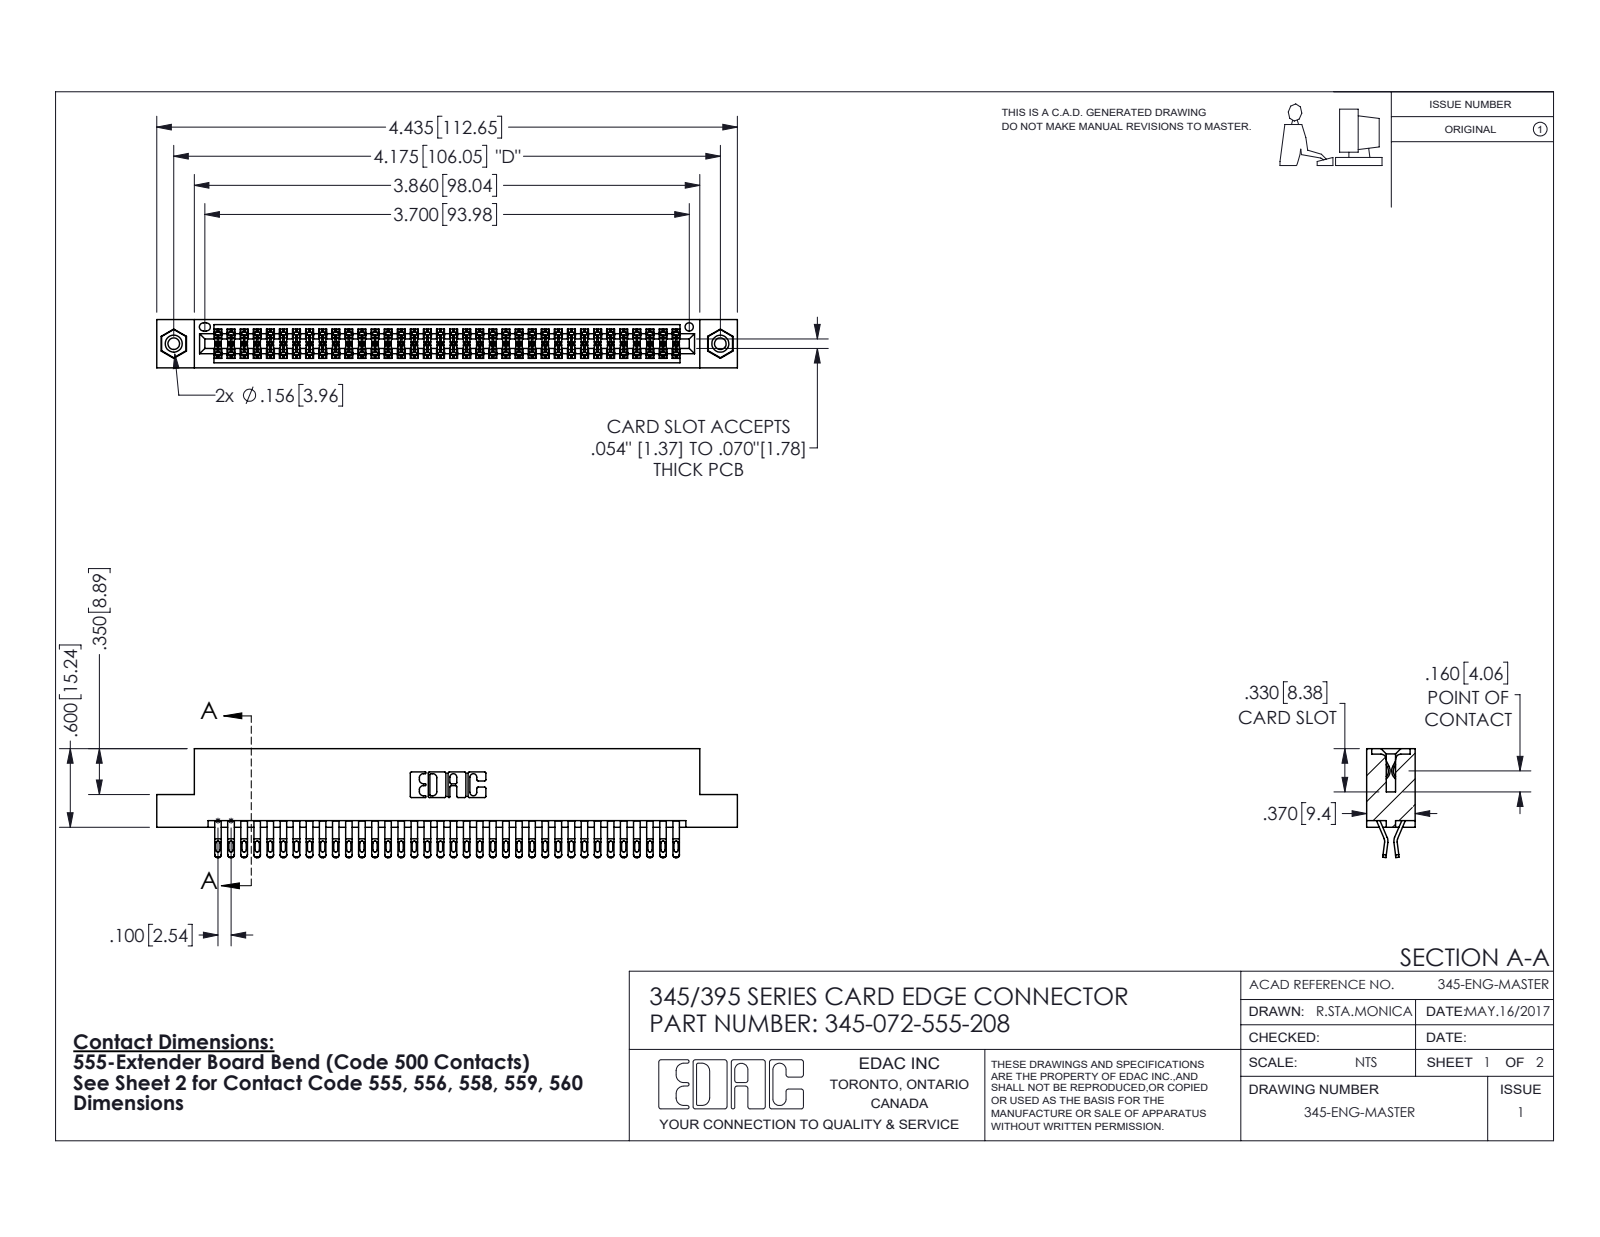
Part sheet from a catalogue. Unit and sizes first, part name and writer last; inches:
Units: inches
Overall size (bounding box): 4.435 × 0.832 × 0.37
Round holes (diameter × count): ⌀0.089 ×2, ⌀0.125 ×2, ⌀0.156 ×2, ⌀0.064 ×1
Round bosses / shafts (diameter × count): ⌀0.155 ×2
Partial cylindrical surfaces — rounded edges, fillets, slot ends (radius × count): R0.016 ×180, R0.02 ×144, R0.006 ×108, R0.01 ×22, R0.007 ×6, R0.031 ×6, R0.026 ×3, R0.01 ×2
Main face-to-face distances: 0.072, 0.298, 0.37, 0.2, 0.025, 0.098, 0.272, 0.225, 0.175, 0.149
Hole centre spacings: 0.27, 3.939, 4.175
Volume: 0.677 in³ · Surface area: 26.37 in²
Bodies: 75 solids, 4218 faces (2344 planar, 1858 cylindrical, 16 other)
Part name (STEP PRODUCT): 345 Part_Flush Mounting Lugs - 0.156 Dia-TI; 345-072-555-208; 345-292-001_555 Tail; 345-250-001_345-250-003-102
STEP written by: SolidWorks 2016 (CONFIG_CONTROL_DESIGN)
